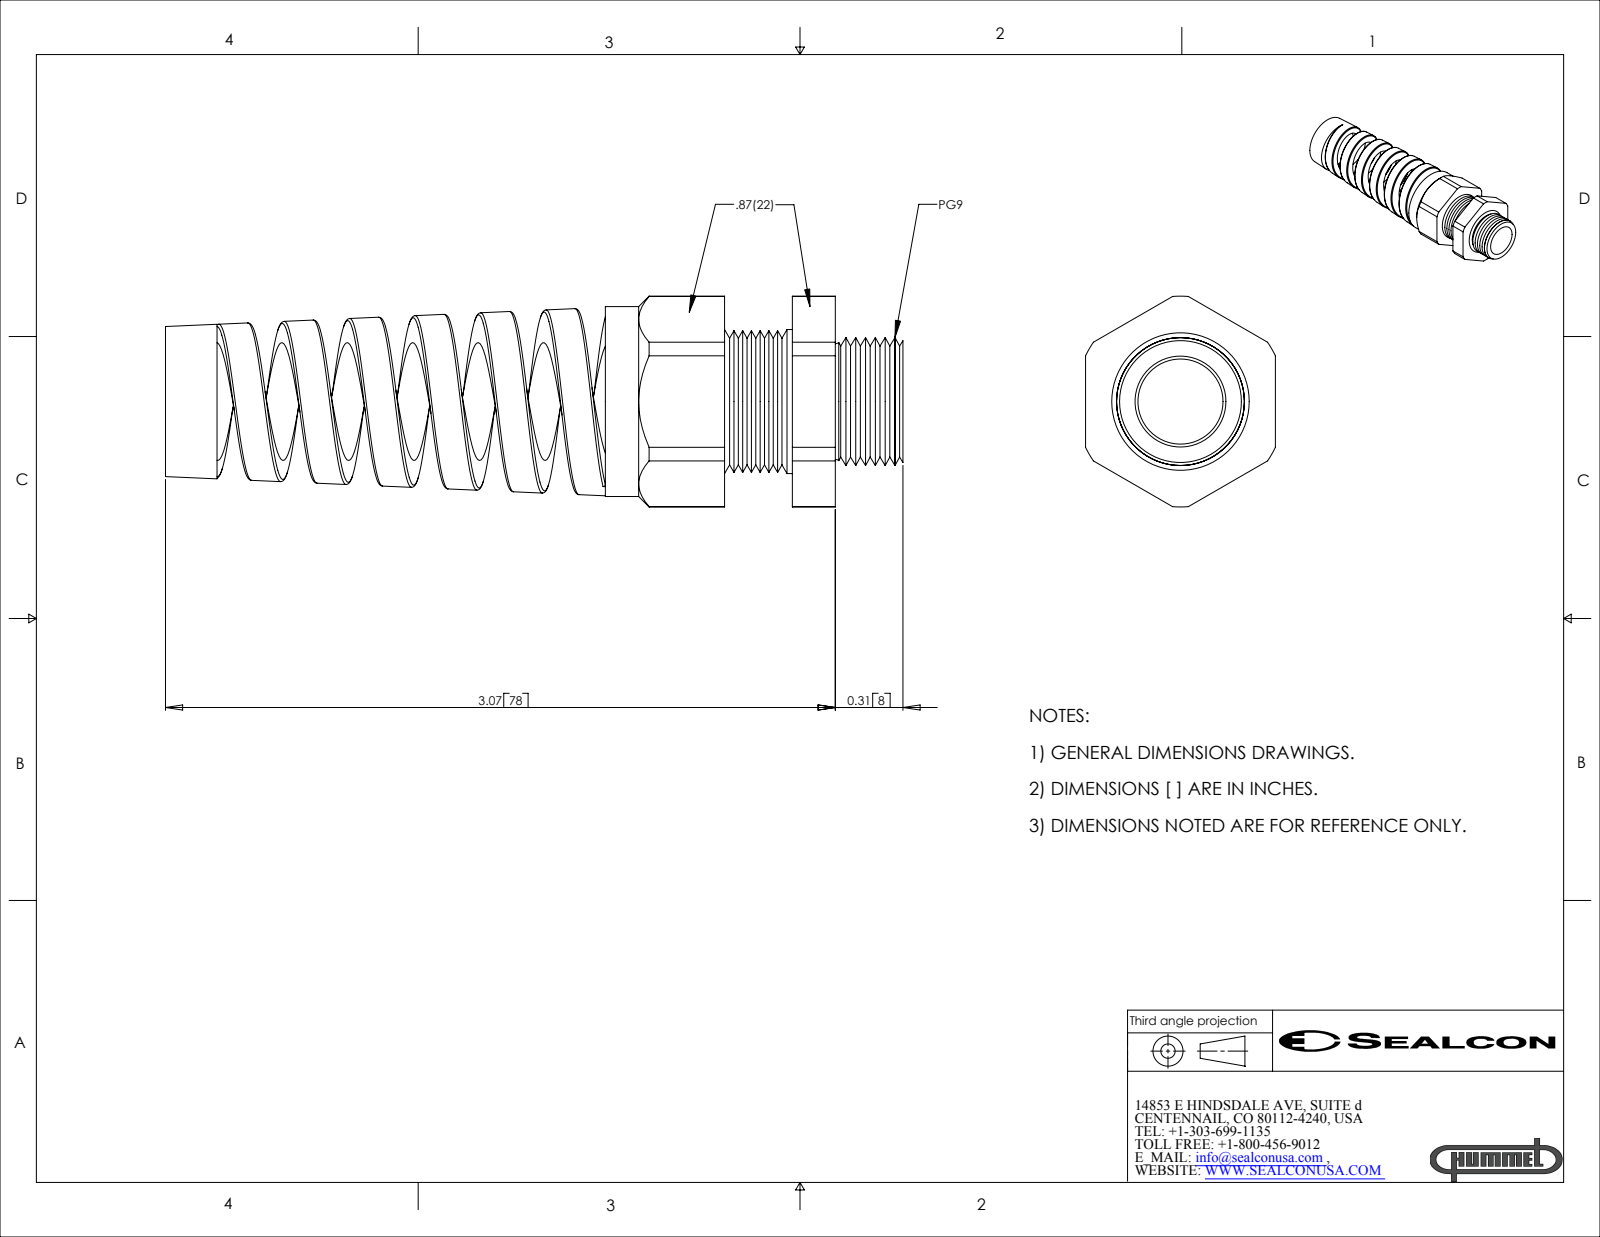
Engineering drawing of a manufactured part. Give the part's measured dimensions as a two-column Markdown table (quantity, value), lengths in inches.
| quantity | value |
| --- | --- |
| part name | CF09GA-BK |
| STEP written by | SolidWorks 2007 (CONFIG_CONTROL_DESIGN) |
| units | inches |
| bodies | 2 solids, 153 faces (24 planar, 37 cylindrical, 92 other) |
| overall size | 3.38 × 0.966 × 0.87 |
| volume | 0.73 in³ |
| surface area | 17.23 in² |
| round holes (diameter × count) | 0.39 × 1, 0.54 × 1 |
| round bosses / shafts (diameter × count) | 0.87 × 1, 0.66 × 1 |
| partial cylindrical surfaces (radius × count) | 0.28 × 1, 0.483 × 1 |
| main face-to-face distances | 0.87, 0.508, 0.311, 0.197, 0.546, 0.857, 1.054, 2.016, 2.562, 2.873 |
